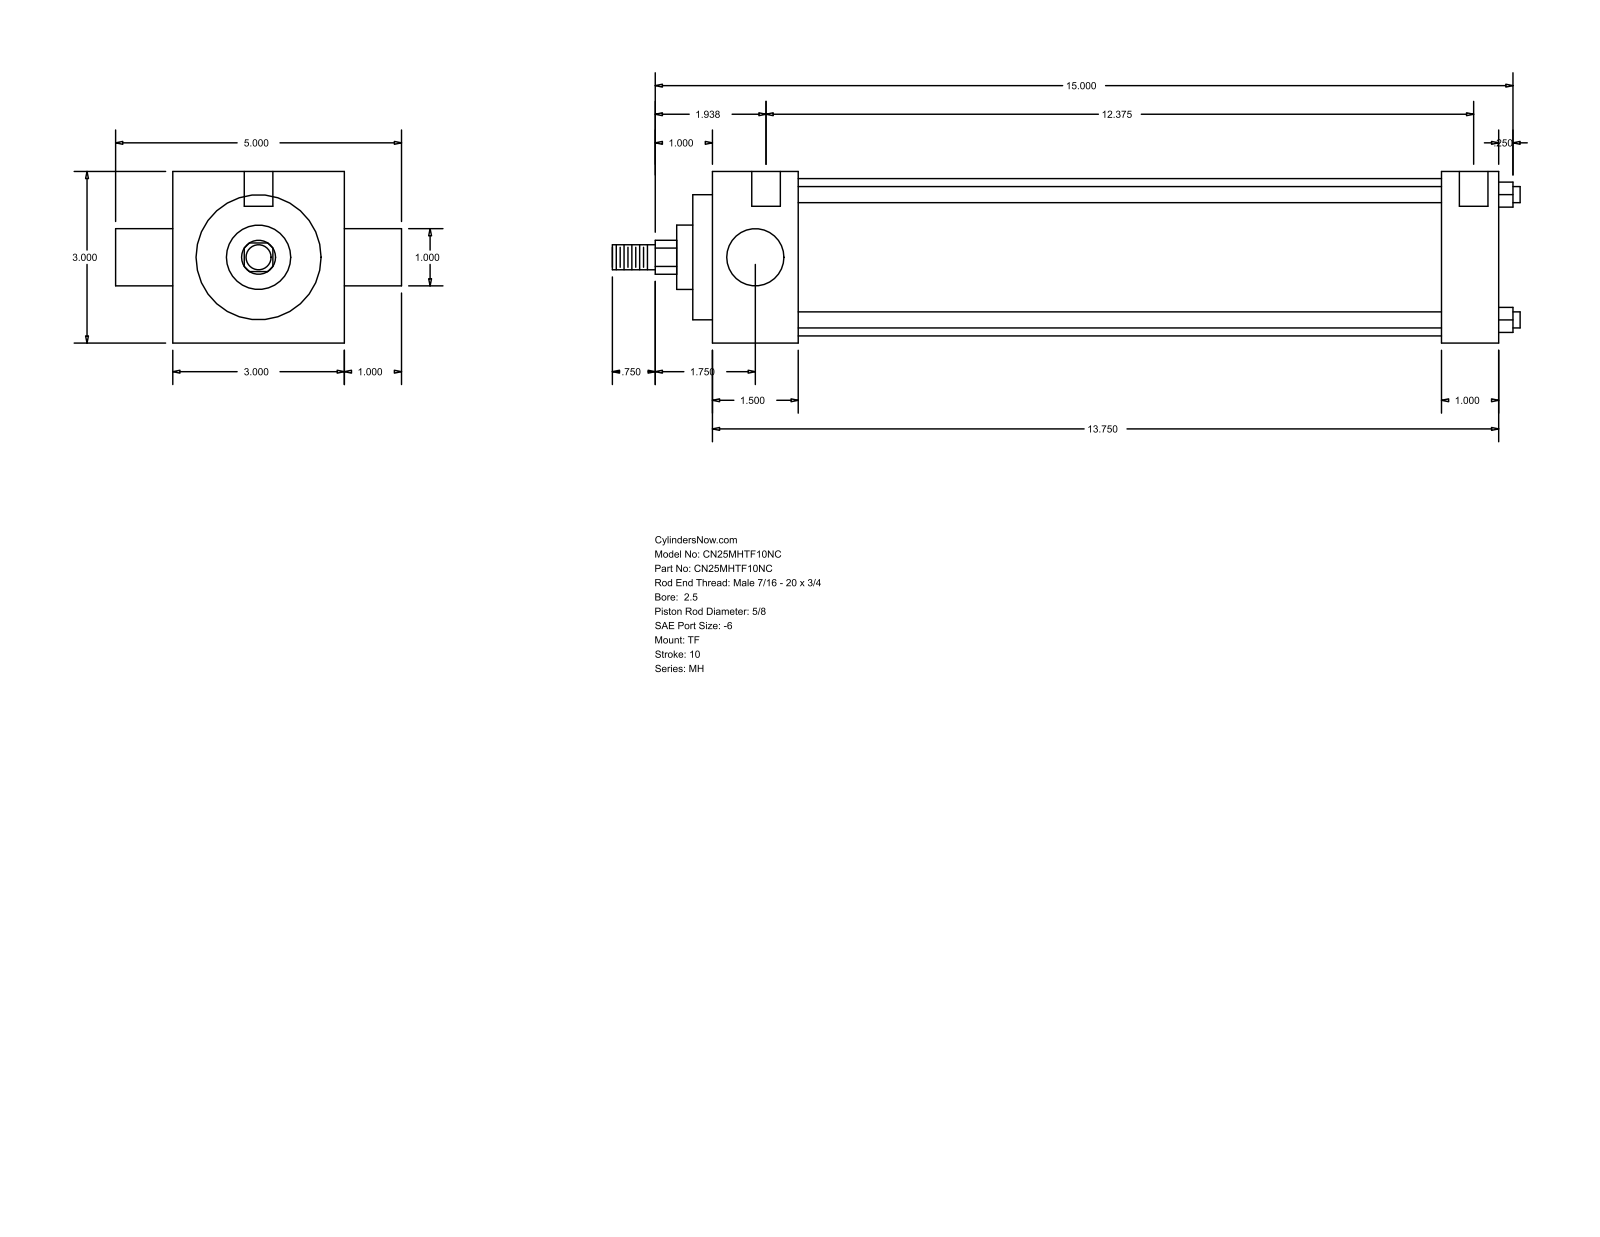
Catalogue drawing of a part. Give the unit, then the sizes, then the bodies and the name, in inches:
Units: inches
Overall size (bounding box): 15.875 × 5 × 3
Round holes (diameter × count): ⌀0.219 ×3, ⌀0.5 ×2
Round bosses / shafts (diameter × count): ⌀0.281 ×4, ⌀2.75 ×1, ⌀2.187 ×1, ⌀1.125 ×1, ⌀1 ×1, ⌀0.625 ×1, ⌀0.437 ×1
Partial cylindrical surfaces — rounded edges, fillets, slot ends (radius × count): R0.297 ×1
Main face-to-face distances: 3, 13.75, 1, 1.5, 12.25, 12.75, 11.25, 0.344, 1.844, 13.094
Hole centre spacings: 0.125, 0.187, 12.375, 12.5, 12.563, 12.687
Bodies: 0 solids, 86 faces (61 planar, 25 cylindrical, 0 other)
Part name (STEP PRODUCT): MH_TF__0250_0.625
STEP written by: GSSL Pune (CONFIG_CONTROL_DESIGN)
